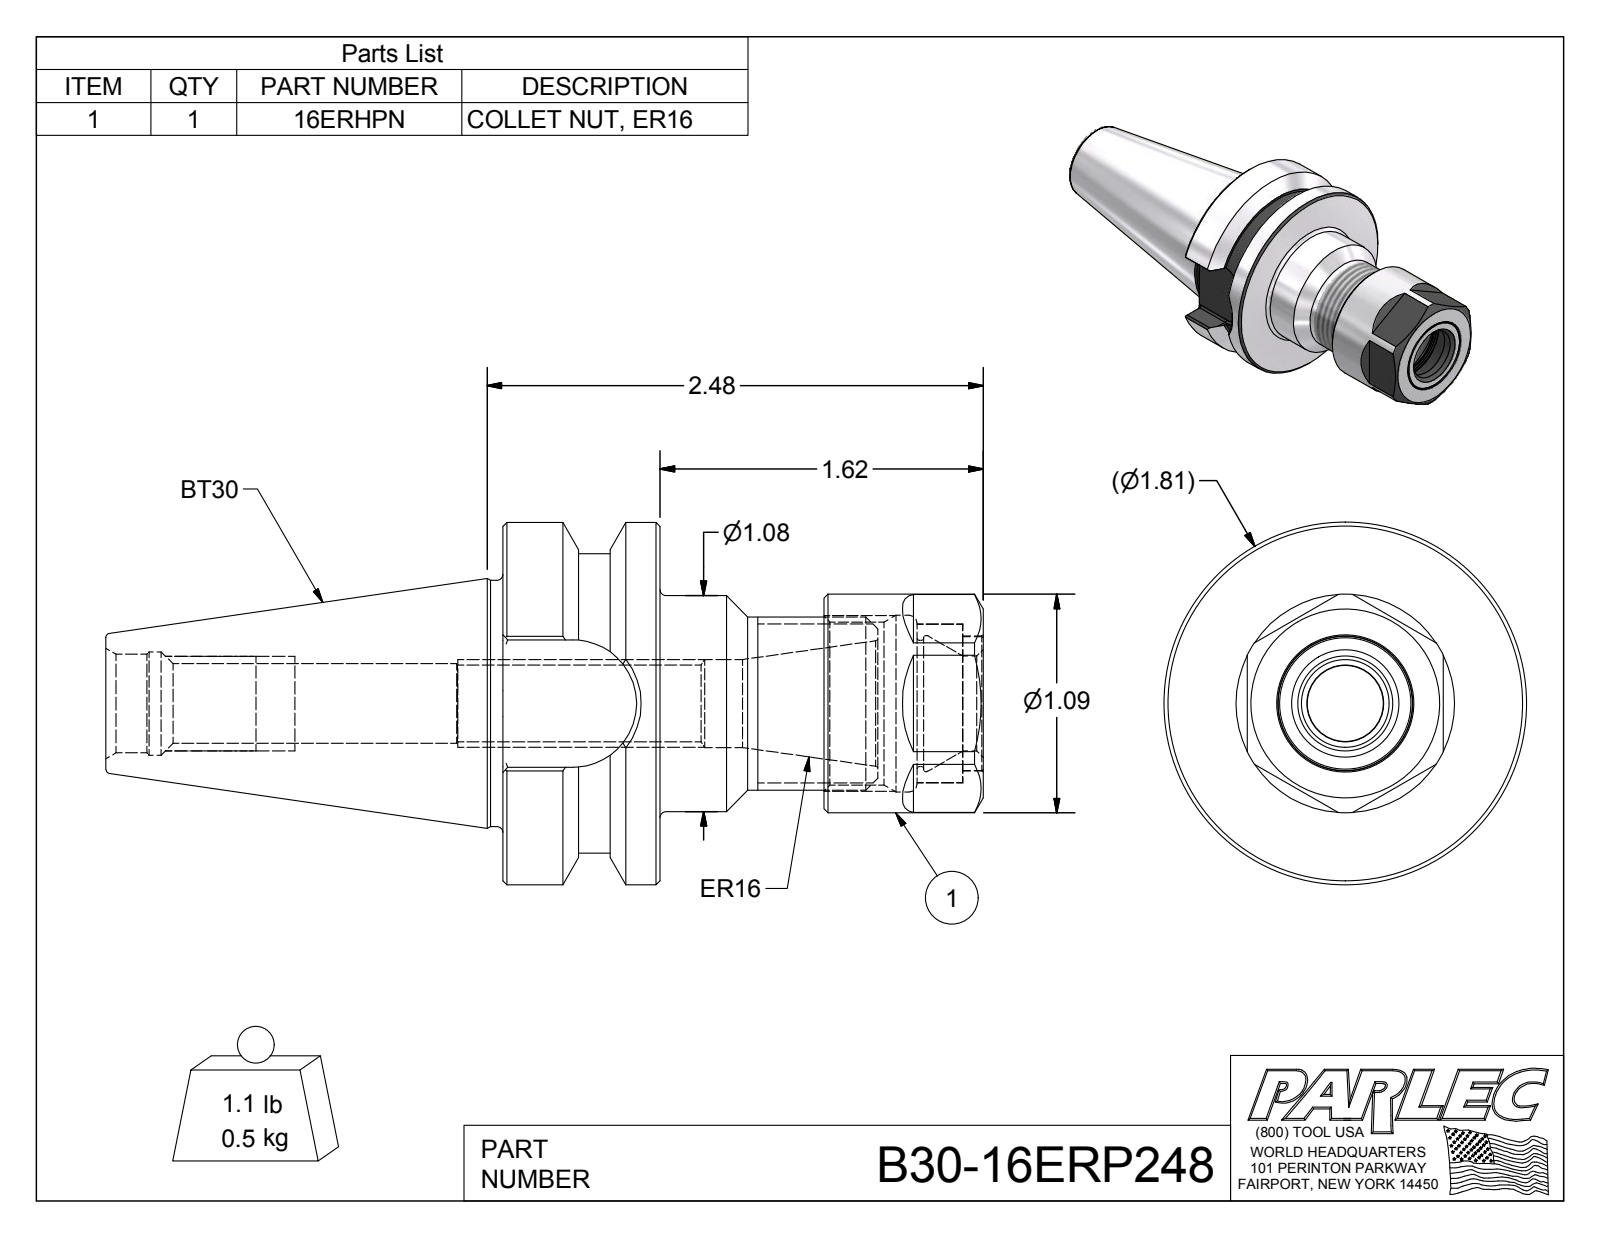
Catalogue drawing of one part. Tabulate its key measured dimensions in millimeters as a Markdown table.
| quantity | value |
| --- | --- |
| part name | B30-16ER236-1; 16ERHPN; B30-16ERP248 |
| STEP written by | Autodesk Inventor 2016 (AUTOMOTIVE_DESIGN) |
| units | millimeters |
| bodies | 3 solids, 115 faces (43 planar, 33 cylindrical, 39 other) |
| overall size | 111.4 × 46 × 46 |
| volume | 62 202 mm³ |
| surface area | 19 877 mm² |
| round holes (diameter × count) | 9.73 × 1, 10.11 × 1, 11.18 × 1, 12.04 × 1, 12.51 × 1, 13.12 × 1, 16 × 1, 17.11 × 1, 17.27 × 1, 20.17 × 1, 20.68 × 1, 22.43 × 1 |
| round bosses / shafts (diameter × count) | 46 × 1, 31.24 × 1, 27.74 × 1, 27.43 × 1, 22 × 1, 20.07 × 1, 17.01 × 1 |
| partial cylindrical surfaces (radius × count) | 0.51 × 8, 8.09 × 1, 19 × 1 |
| main face-to-face distances | 19.99, 24.9, 61.01, 41.02, 32.6, 3.85, 28.75, 40.79, 20.8, 20.22 |
